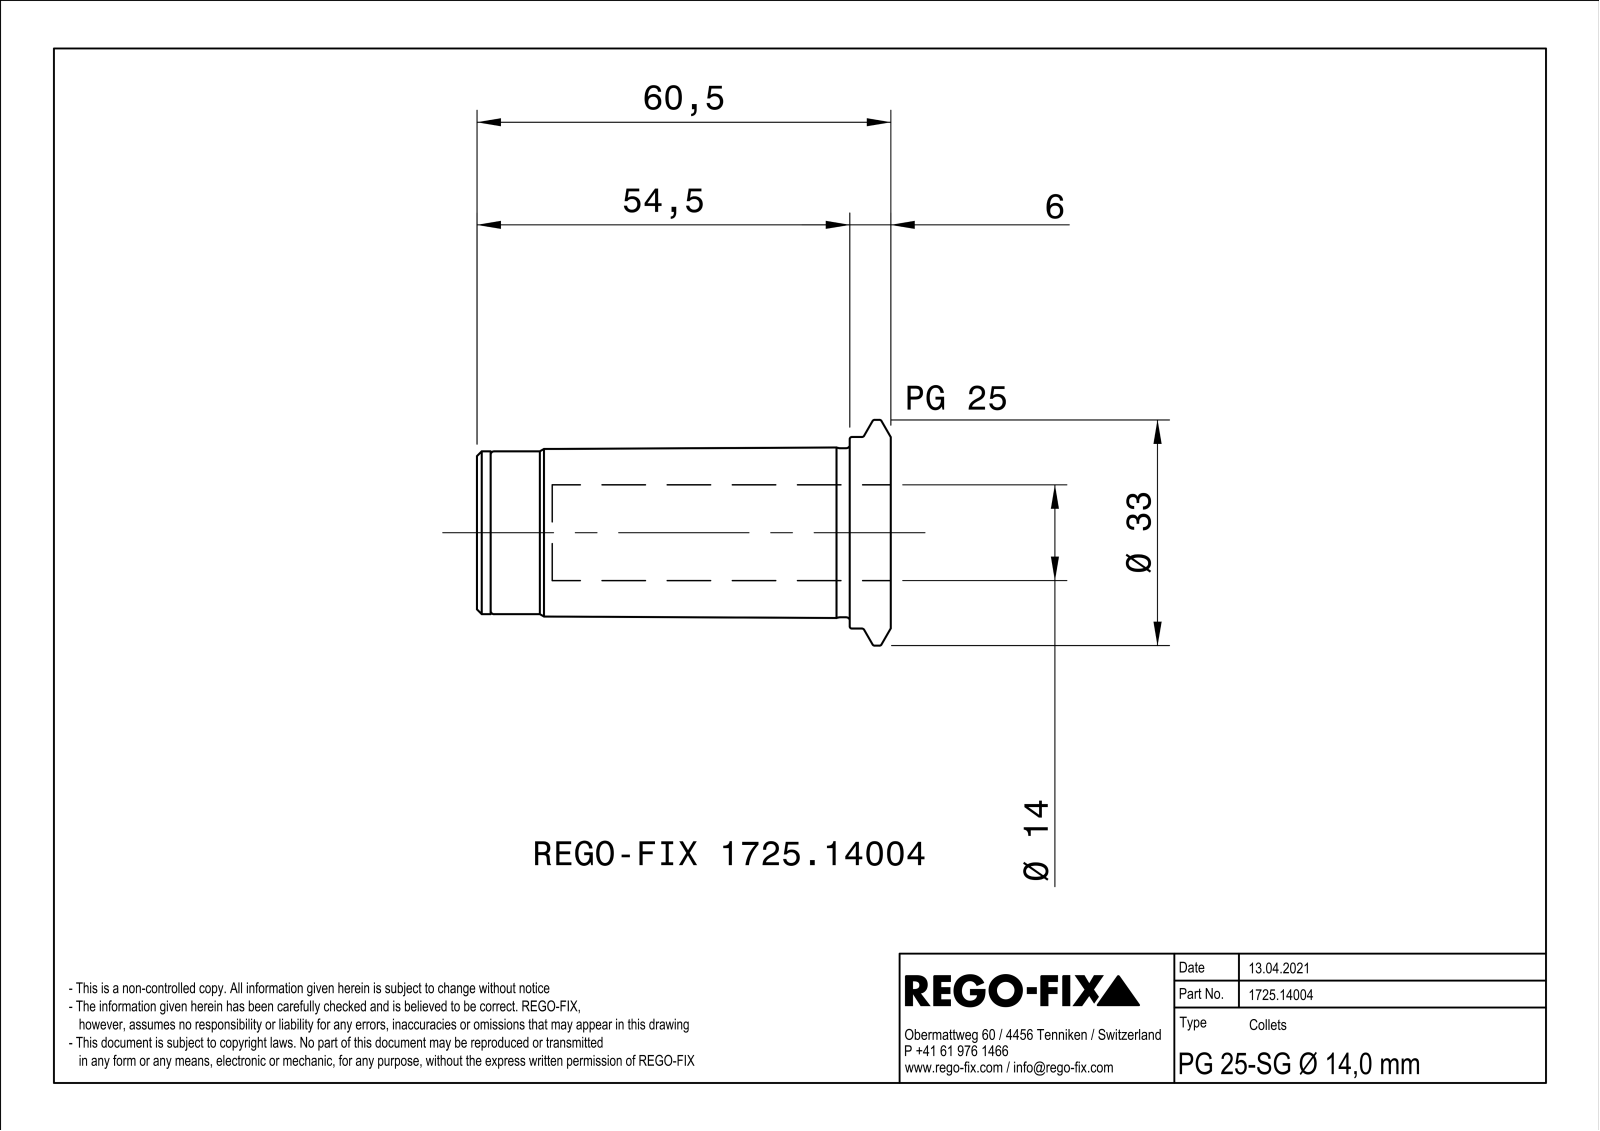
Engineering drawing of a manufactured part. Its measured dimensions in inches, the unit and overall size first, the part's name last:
Units: inches
Overall size (bounding box): 2.382 × 1.299 × 1.299
Round holes (diameter × count): ⌀0.098 ×3, ⌀0.205 ×1, ⌀0.272 ×1, ⌀0.323 ×1, ⌀0.551 ×1, ⌀0.803 ×1, ⌀0.824 ×1, ⌀0.874 ×1
Round bosses / shafts (diameter × count): ⌀1.299 ×1, ⌀1.102 ×1, ⌀0.972 ×1, ⌀0.937 ×1, ⌀0.472 ×1
Main face-to-face distances: 0.039, 2.382, 2.071, 0.311, 2.303, 0.232, 0.079, 1.969, 0.102, 0.335
Hole centre spacings: 0.305, 0.529, 0.528
Bodies: 1 solid, 85 faces (23 planar, 23 cylindrical, 39 other)
Part name (STEP PRODUCT): NOCUT
STEP written by: SIEMENS PLM Software Solid Edge ST10 (AUTOMOTIVE_DESIGN)
